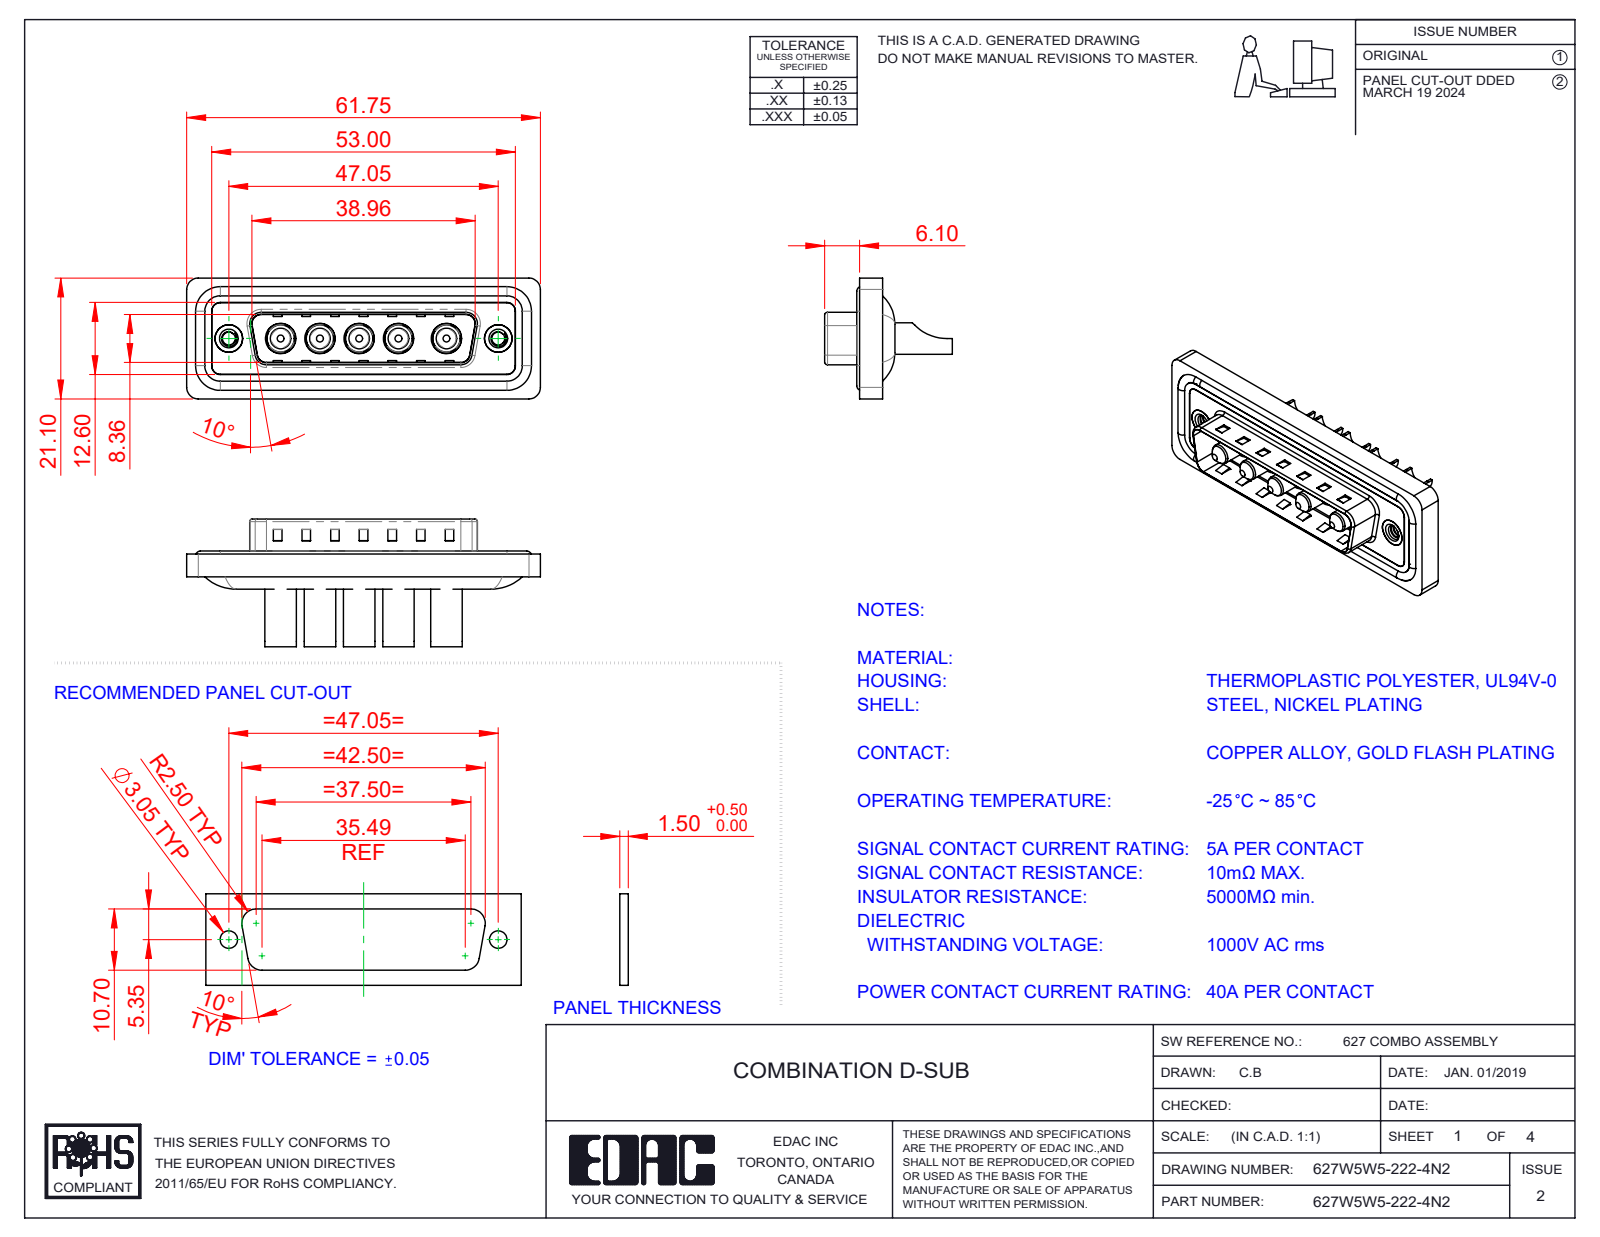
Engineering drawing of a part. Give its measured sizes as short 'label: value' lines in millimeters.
name: 627Combo Shell Rear_25 Contacts; 627Combo Threaded Rivet_2; Power Pin_40A SC; 627Combo Waterproof Housing_25 Contacts (+3 more)
written by: SolidWorks 2023 (CONFIG_CONTROL_DESIGN)
unit: mm
bodies: 17 solids, 698 faces (269 planar, 288 cylindrical, 141 other)
size: 61.75 × 22.3 × 21.1
volume: 7 672 mm³; area: 12 496 mm²
holes: 5× ⌀4.6, 5× ⌀4.85, 5× ⌀5.3, 2× ⌀2.26, 2× ⌀4, 2× ⌀4.8, 2× ⌀5
bosses: 5× ⌀5.5, 5× ⌀5.2, 5× ⌀4.75, 5× ⌀3.75, 5× ⌀3.6, 4× ⌀1.6, 2× ⌀4.9
rounds: 22× R1.5, 18× R2, 8× R0.5, 8× R1.6, 5× R2.1, 4× R0.25, 4× R0.6, 4× R0.65
face distances: 0.4, 0.5, 1.1, 1.5, 3.1, 1.6, 2.9, 0.82, 9.58, 5.65
hole spacings: 6.86, 9.04, 13.73, 38.01, 6.87, 8.37, 8.38, 9.05
